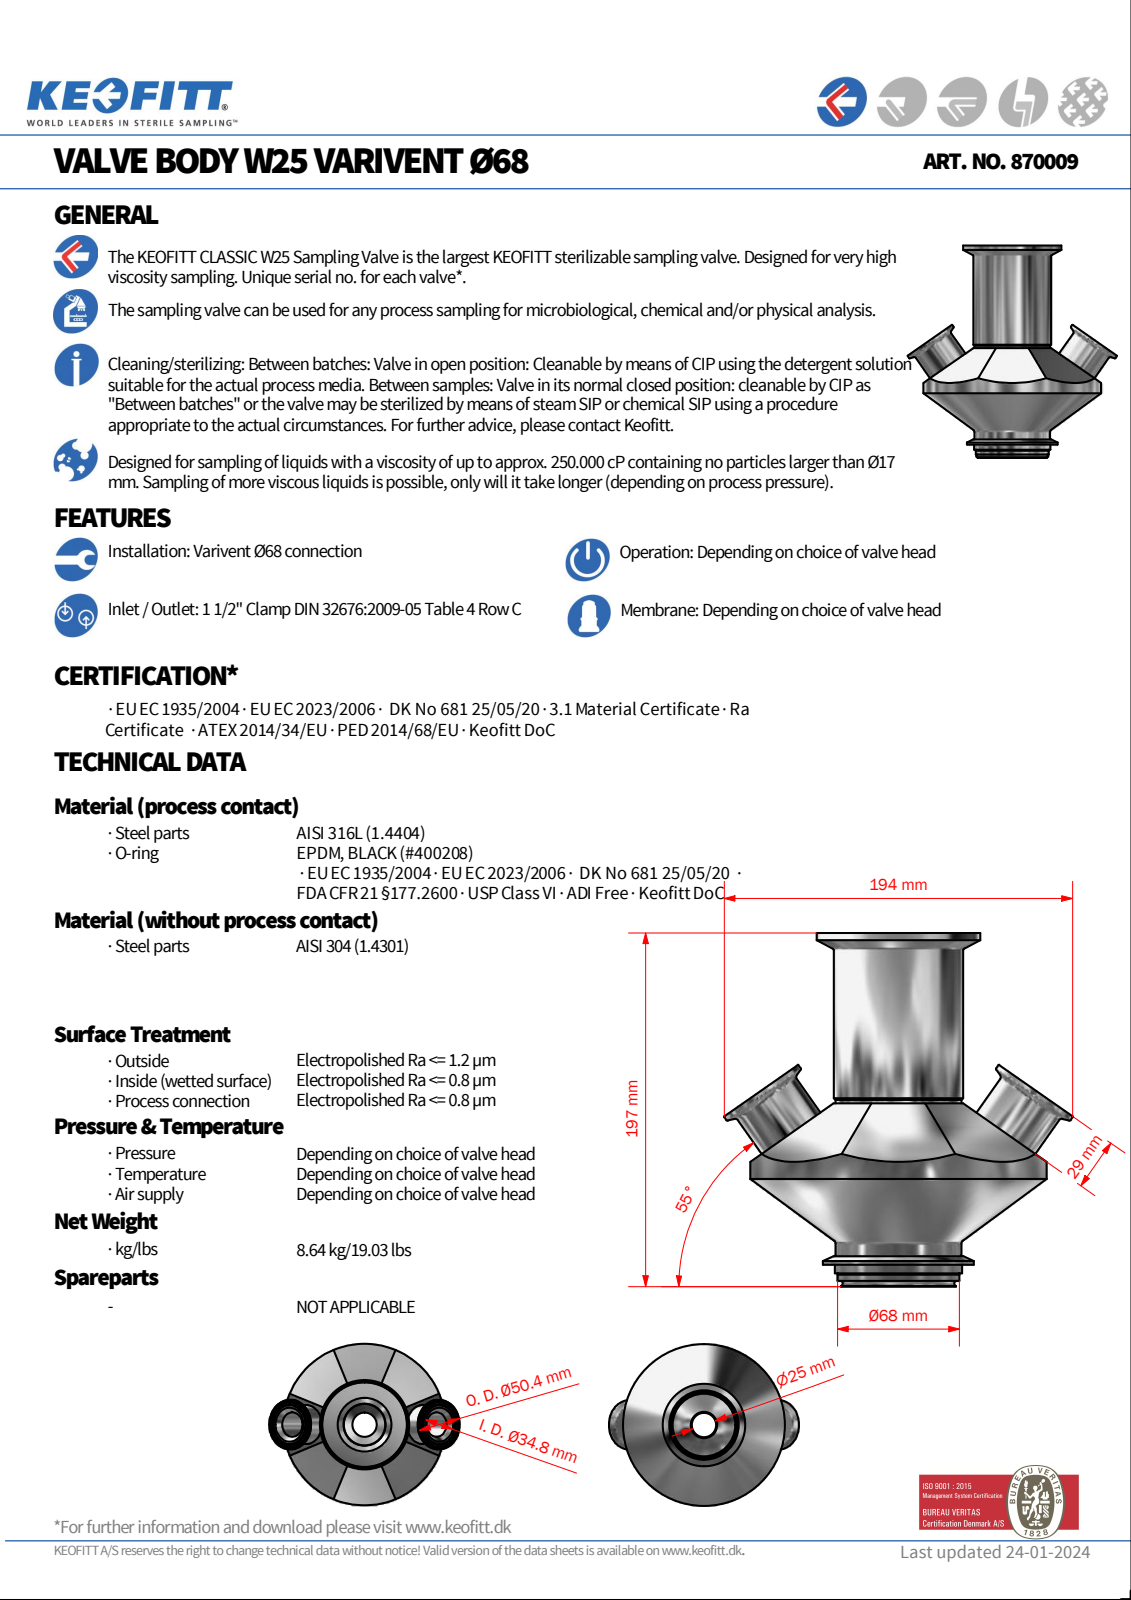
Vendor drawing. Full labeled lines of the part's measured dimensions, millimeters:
Part name (STEP PRODUCT): 870009
STEP written by: Autodesk Inventor 2022 (AUTOMOTIVE_DESIGN)
Units: millimetres
Bodies: 1 solid, 48 faces (17 planar, 13 cylindrical, 18 other)
Overall size (bounding box): 197 × 194.11 × 165
Volume: 1 581 000 mm³ · Surface area: 101 139 mm²
Round bosses / shafts (diameter × count): ⌀50.4 ×2, ⌀40 ×2, ⌀165 ×1, ⌀91 ×1, ⌀84 ×1, ⌀72 ×1, ⌀70.85 ×1, ⌀70 ×1
Main face-to-face distances: 197, 28.99, 12.25, 184.75, 102, 89.75, 95, 4.75, 7.5, 94.5
